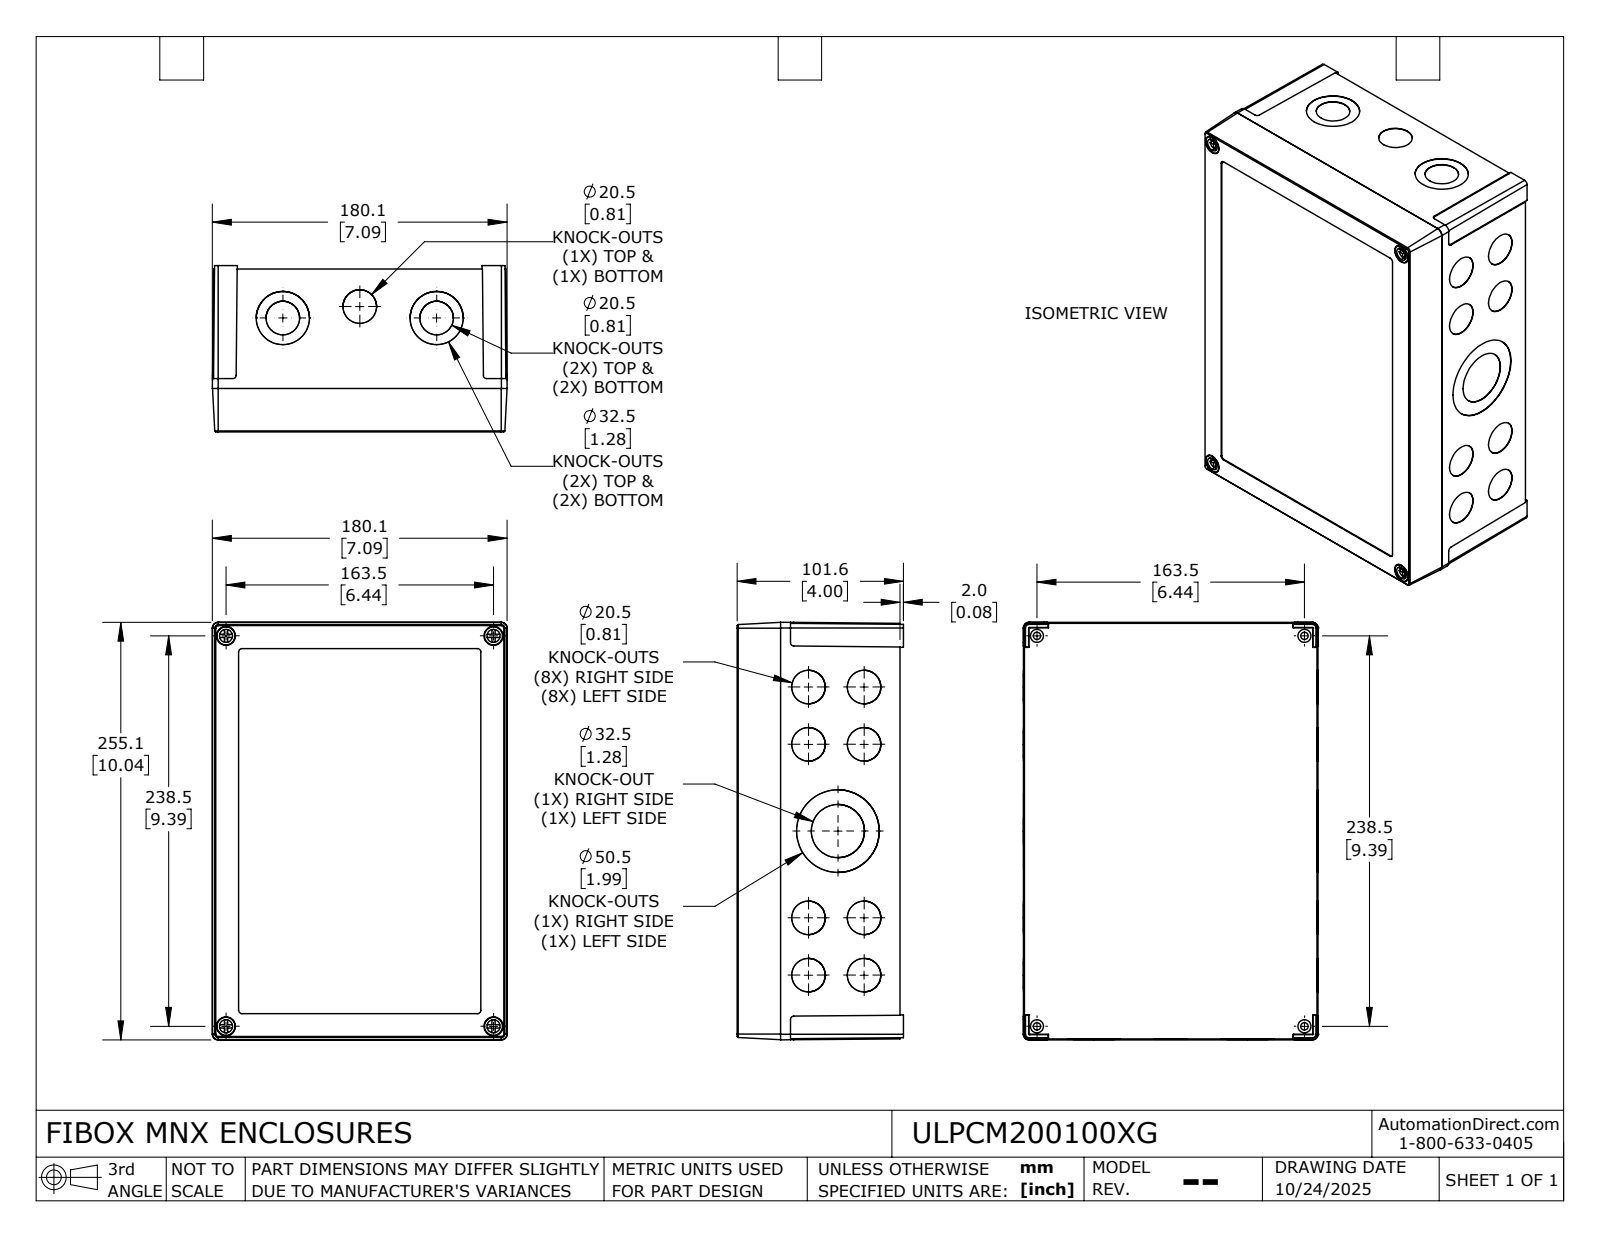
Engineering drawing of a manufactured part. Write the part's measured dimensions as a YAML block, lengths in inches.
part_name: "ULPCM200100XG_Default"
step_written_by: "SolidWorks 2024 (CONFIG_CONTROL_DESIGN)"
units: inches
bodies: {solids: 6, faces: 720, planar: 392, cylindrical: 284, other: 44}
overall_size: [10.043, 7.091, 4]
volume: 36.22
surface_area: 568
round_holes:
  - {diameter: 0.807, count: 22}
  - {diameter: 0.126, count: 20}
  - {diameter: 0.157, count: 20}
  - {diameter: 1.28, count: 6}
  - {diameter: 0.177, count: 4}
  - {diameter: 0.315, count: 4}
  - {diameter: 0.457, count: 4}
  - {diameter: 1.988, count: 2}
round_bosses_or_shafts:
  - {diameter: 0.315, count: 16}
  - {diameter: 0.098, count: 8}
  - {diameter: 0.433, count: 4}
  - {diameter: 0.283, count: 4}
  - {diameter: 0.276, count: 4}
partial_cylinders:
  - {radius: 0.079, count: 8}
  - {radius: 0.112, count: 6}
  - {radius: 0.042, count: 4}
  - {radius: 0.197, count: 4}
  - {radius: 0.046, count: 2}
face_to_face_distances: [3.815, 0.165, 0.118, 3.697, 0.087, 3.902, 3.783, 3.921, 3.803, 0.02]
hole_center_spacings: [1.378, 1.339, 1.921, 1.939, 5.046, 5.551, 5.71, 4.921]
